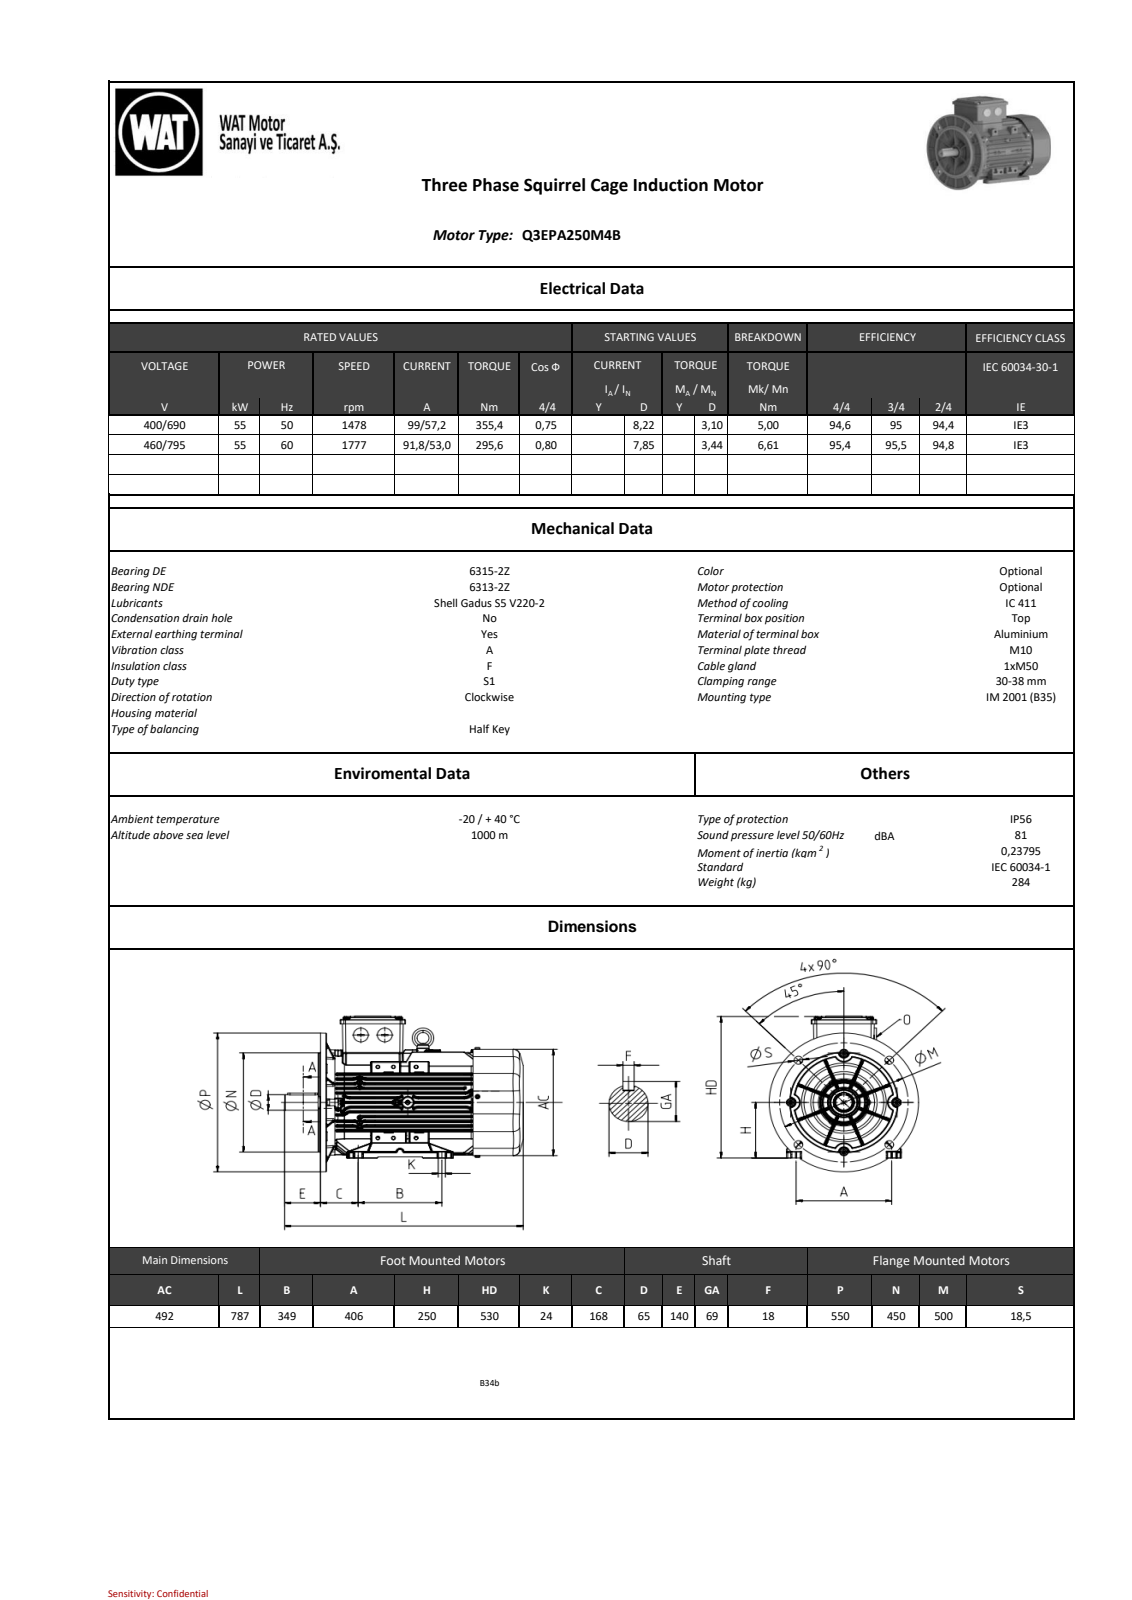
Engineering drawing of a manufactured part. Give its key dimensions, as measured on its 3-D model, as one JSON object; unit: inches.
{"part_name": "001_objects", "step_written_by": "SIEMENS PLM Software NX2206.8101 (AUTOMOTIVE_DESIGN)", "units": "inches", "bodies": {"solids": 0, "faces": 15553, "planar": 7154, "cylindrical": 4081, "other": 4318}, "overall_size": [30.984, 21.949, 21.654], "round_holes": [[0.335, 13], [0.36, 12], [0.402, 11], [0.236, 8], [0.748, 8], [0.028, 6], [0.197, 5], [0.295, 5], [0.433, 5], [0.728, 5], [0.169, 4], [0.217, 4]], "round_bosses_or_shafts": [[0.394, 18], [0.619, 12], [0.713, 11], [0.315, 6], [0.583, 4], [0.501, 4], [0.197, 4], [0.23, 3]], "partial_cylinders_radius": [[0.039, 966], [0.008, 356], [0.079, 336], [0.02, 271], [0.197, 255], [0.098, 150], [0.157, 97], [0.012, 52]], "face_to_face_distances": [0.315, 0.354, 7.473, 0.611, 6.655, 0.818, 0.584, 7.267, 0.118, 0.206], "hole_center_spacings": [5.761, 6.707, 9.096, 11.667, 13.186, 6.142, 2.684, 7.533]}
